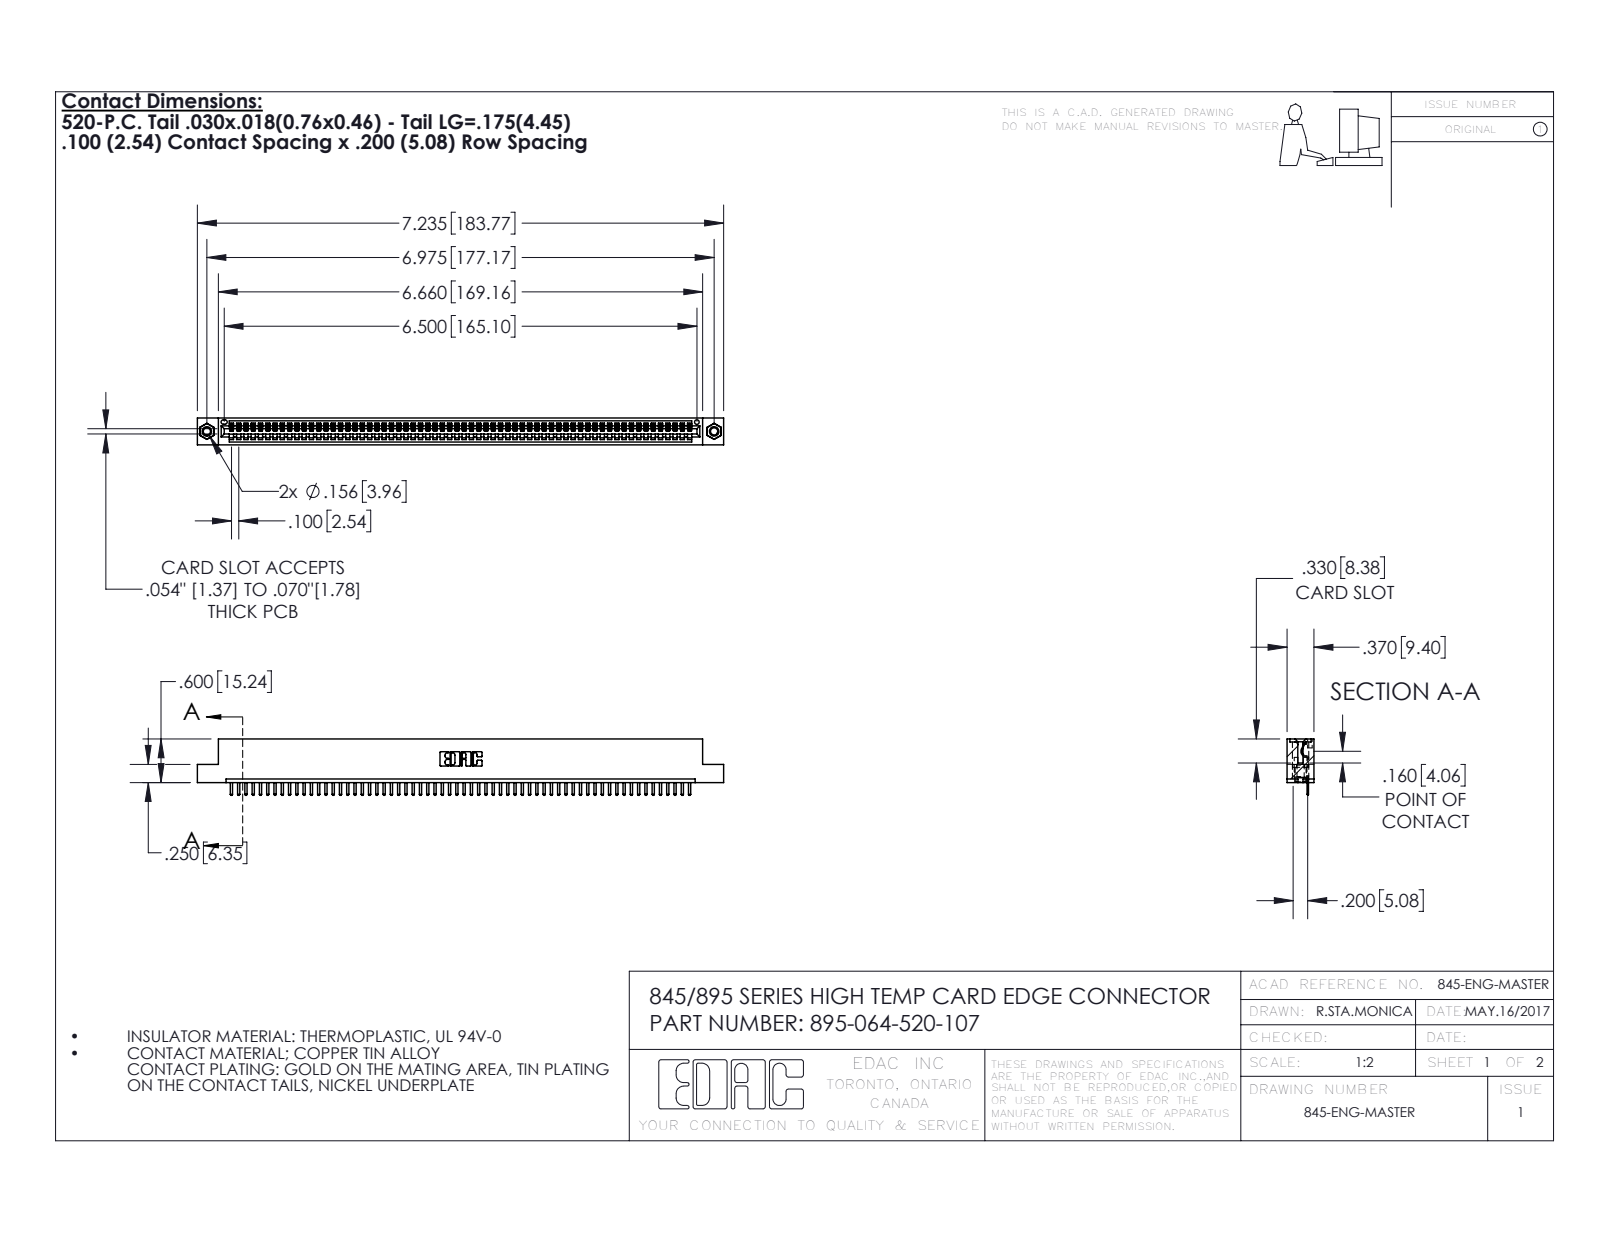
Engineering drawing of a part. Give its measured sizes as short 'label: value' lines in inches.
name: 395-064-520-107; 345-250-001_345-250-005-103; 345 Part_Flush Mounting Lugs - 0.156 Dia-TI; 345-292-001_345-293-120
written by: SolidWorks 2016 (CONFIG_CONTROL_DESIGN)
unit: in
bodies: 67 solids, 4154 faces (2800 planar, 1338 cylindrical, 16 other)
size: 7.235 × 0.775 × 0.37
volume: 1.064 in³; area: 35.5 in²
holes: 2× ⌀0.098, 2× ⌀0.125, 2× ⌀0.156, 1× ⌀0.064
bosses: 2× ⌀0.155
rounds: 130× R0.01, 128× R0.006, 22× R0.01, 6× R0.007, 6× R0.031, 3× R0.026, 2× R0.031, 2× R0.04
face distances: 0.072, 0.298, 0.37, 0.2, 0.098, 0.272, 0.025, 0.225, 0.072, 0.149
hole spacings: 0.27, 6.739, 6.975
